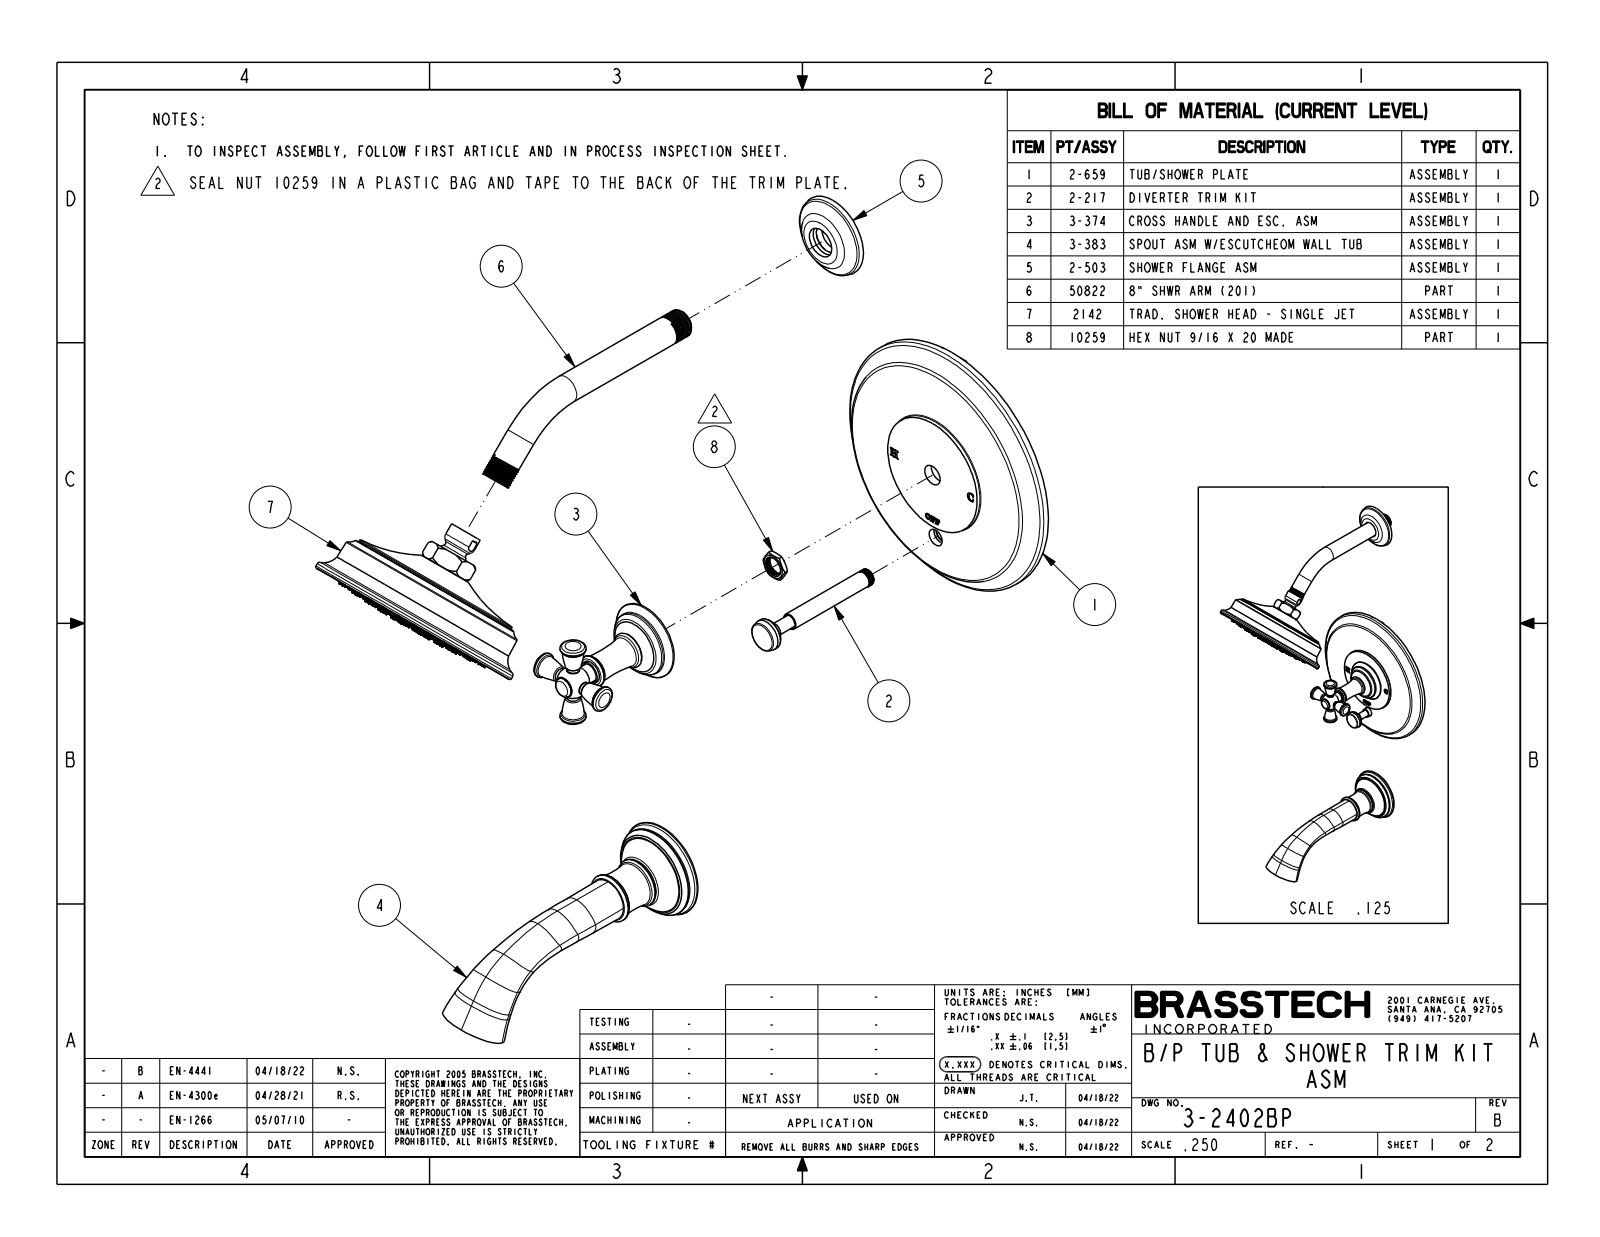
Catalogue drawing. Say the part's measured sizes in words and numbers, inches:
The part is named "3-2402BP". Its 3-D file was written by "CREO PARAMETRIC BY PTC INC, 2018400 (CONFIG_CONTROL_DESIGN)". It is 3 solids with 1379 faces: 277 planar, 250 cylindrical and 852 other. Overall it measures 20.973 by 10.691 by 7.5 inches. Its volume is 81.84 cubic inches and its surface area 280 square inches. Round holes: 90 of diameter 0.05, 1 of diameter 0.22, 1 of diameter 0.604, 1 of diameter 5.275. Round bosses or shafts: 2 of diameter 0.9, 2 of diameter 0.813, 2 of diameter 0.72, 2 of diameter 0.36, 1 of diameter 7.5, 1 of diameter 6.2, 1 of diameter 5.22, 1 of diameter 4.83. The main face-to-face distances are 0.625, 0.75, 0.125, 0.48, 0.145, 0.27, 1.014, 1.897, 1.417, 1.272. The hole center spacings are 1.41, 0.98, 1.41, 0.965, 2.65, 0.49, 2.16, 2.777.
